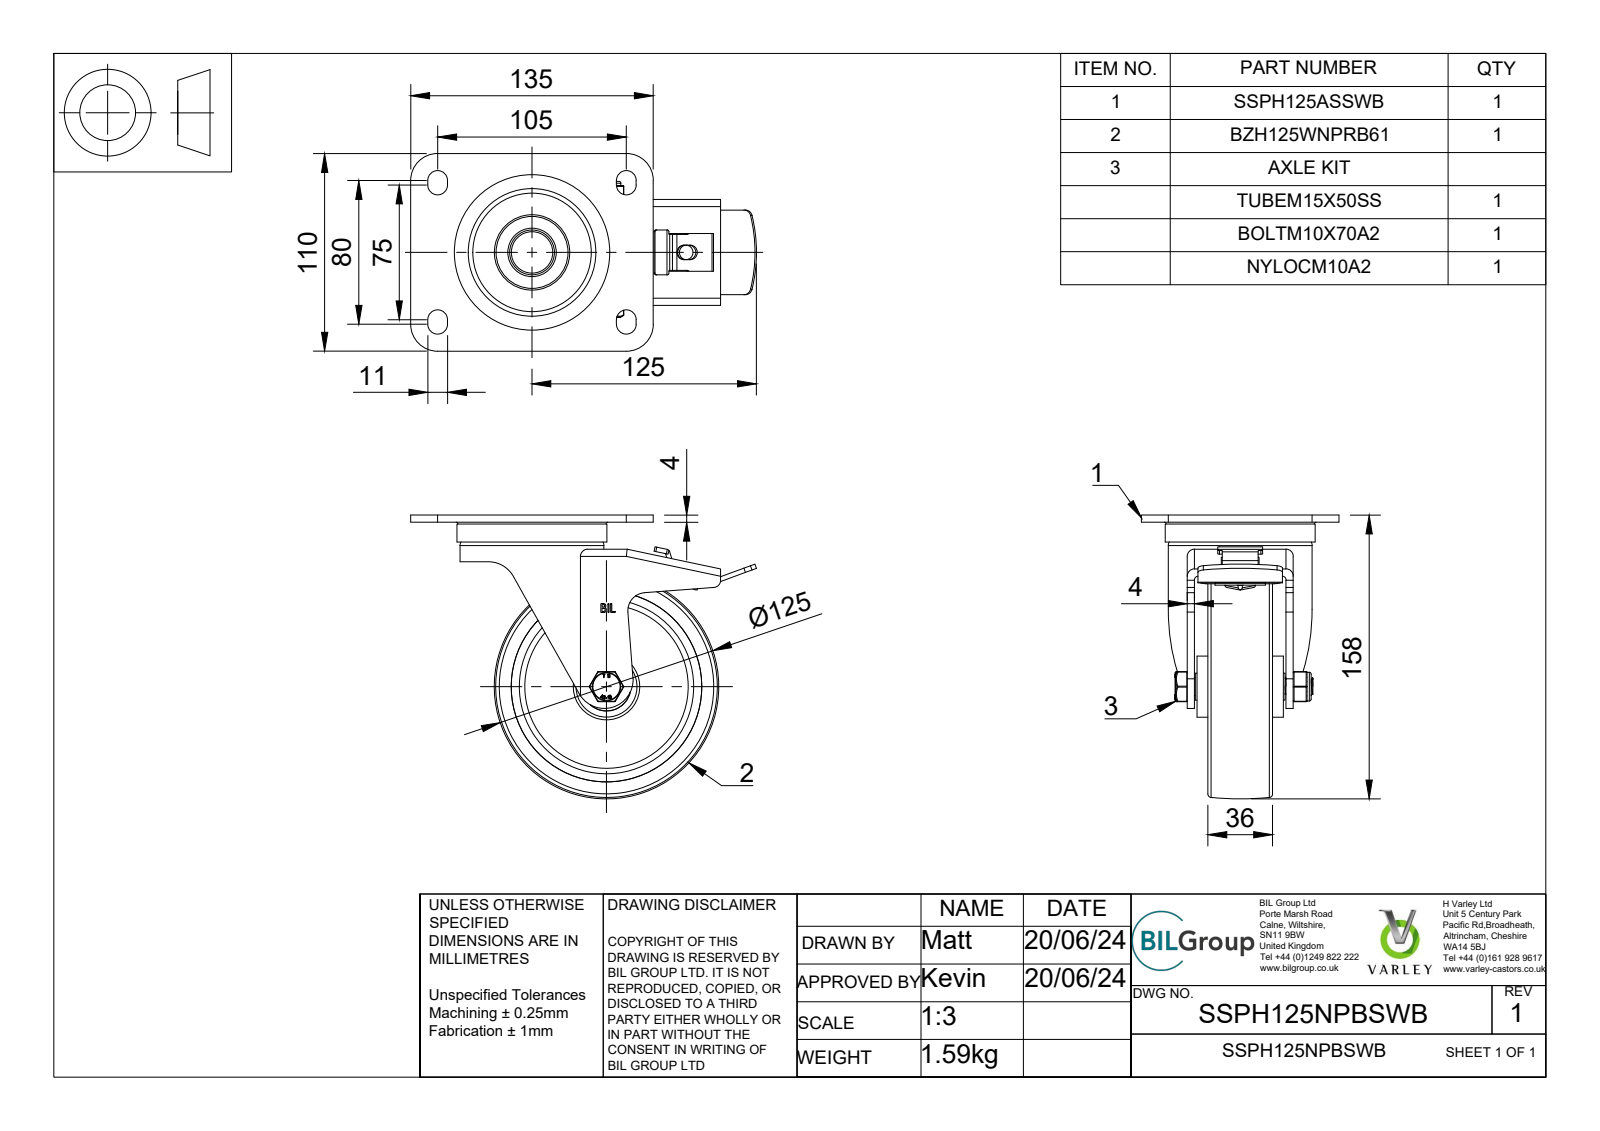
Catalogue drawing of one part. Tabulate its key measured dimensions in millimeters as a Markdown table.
| quantity | value |
| --- | --- |
| part name | SSPH125NPBSWB v3; SSPH125ASSWB v1; STAINLESS STEEL TOP PLATE; STAINLESS STEEL FORKS (+8 more) |
| STEP written by | Autodesk Translation Framework v13.14.0.145 (AUTOMOTIVE_DESIGN) |
| units | millimeters |
| bodies | 24 solids, 779 faces (451 planar, 212 cylindrical, 116 other) |
| overall size | 192.5 × 158 × 110 |
| volume | 433 072 mm³ |
| surface area | 198 433 mm² |
| round holes (diameter × count) | 8 × 1, 10 × 1, 10.2 × 1, 10.5 × 1, 12 × 1, 15.2 × 1, 15.5 × 1, 23.5 × 1, 26 × 1, 27.2 × 1, 32 × 1, 60 × 1 |
| round bosses / shafts (diameter × count) | 4 × 9, 83.5 × 1, 80 × 1, 51 × 1, 34 × 1, 28 × 1, 27 × 1, 25 × 1 |
| partial cylindrical surfaces (radius × count) | 0.5 × 28, 4 × 12, 1.5 × 10, 5.5 × 8, 2 × 7, 1 × 6, 6 × 5, 15 × 4 |
| main face-to-face distances | 4, 13, 9, 6, 21, 15, 11.5, 7.5, 32.5, 26.5 |
